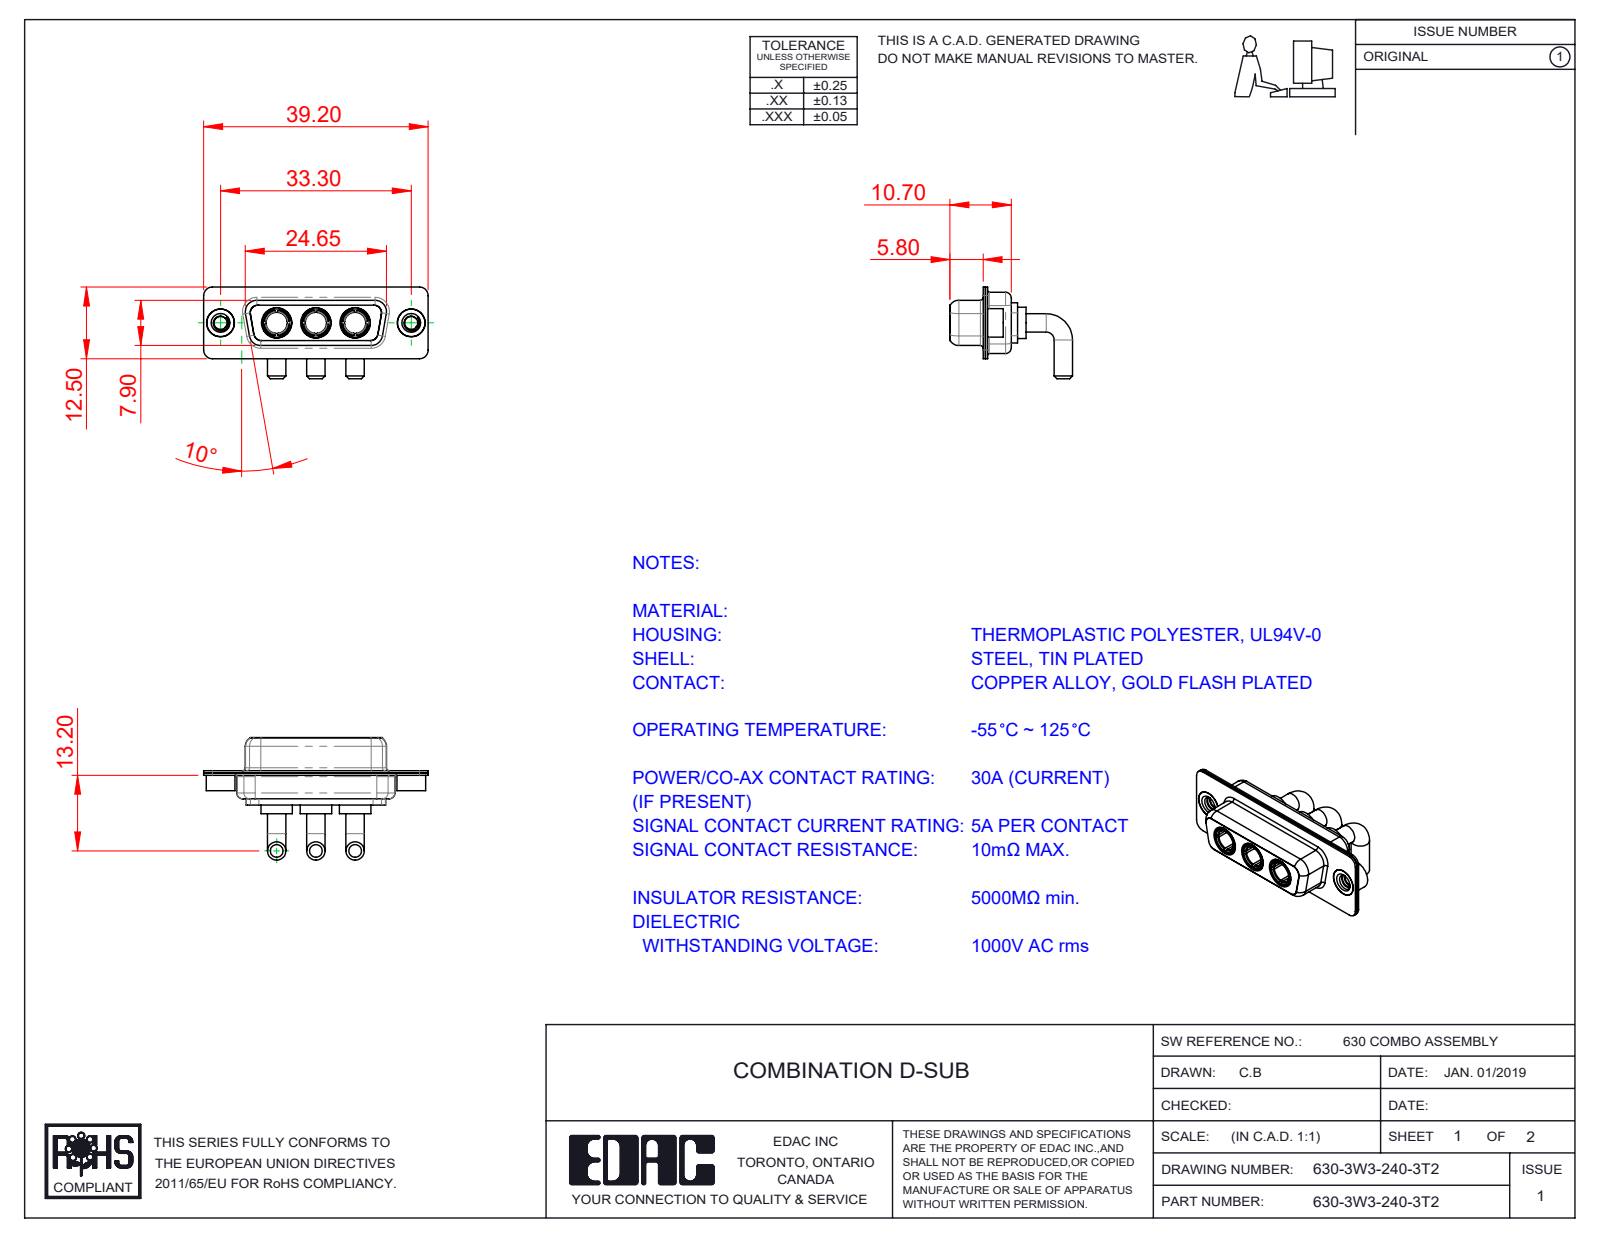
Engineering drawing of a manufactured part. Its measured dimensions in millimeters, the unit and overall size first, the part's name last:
Units: millimetres
Overall size (bounding box): 39.2 × 21.4 × 16
Round holes (diameter × count): ⌀4.85 ×5, ⌀3.7 ×3, ⌀5.3 ×3, ⌀2.26 ×2, ⌀4 ×2, ⌀4.05 ×2
Round bosses / shafts (diameter × count): ⌀3.2 ×6, ⌀5.5 ×3, ⌀5.2 ×3, ⌀4.96 ×3, ⌀4.75 ×3, ⌀3.75 ×3, ⌀5 ×2, ⌀4.95 ×2
Partial cylindrical surfaces — rounded edges, fillets, slot ends (radius × count): R1.5 ×16, R1.35 ×12, R2 ×12, R1.6 ×8, R0.25 ×4, R0.5 ×4, R0.6 ×4, R0.65 ×4
Main face-to-face distances: 0.4, 1.4, 0.45, 8.45, 8.9, 1.8, 6.2, 7.05, 0.8, 7.5
Hole centre spacings: 6.85, 9.8, 16.65, 23.5, 13.7, 33.3
Volume: 2 727 mm³ · Surface area: 5 980 mm²
Bodies: 11 solids, 513 faces (154 planar, 212 cylindrical, 147 other)
Part name (STEP PRODUCT): 630Combo Threaded Rivet_2; Power Socket_30A RA; 630-3W3-240-3T2; 630Combo Shell Rear_15 Contacts (+2 more)
STEP written by: SolidWorks 2020 (CONFIG_CONTROL_DESIGN)
